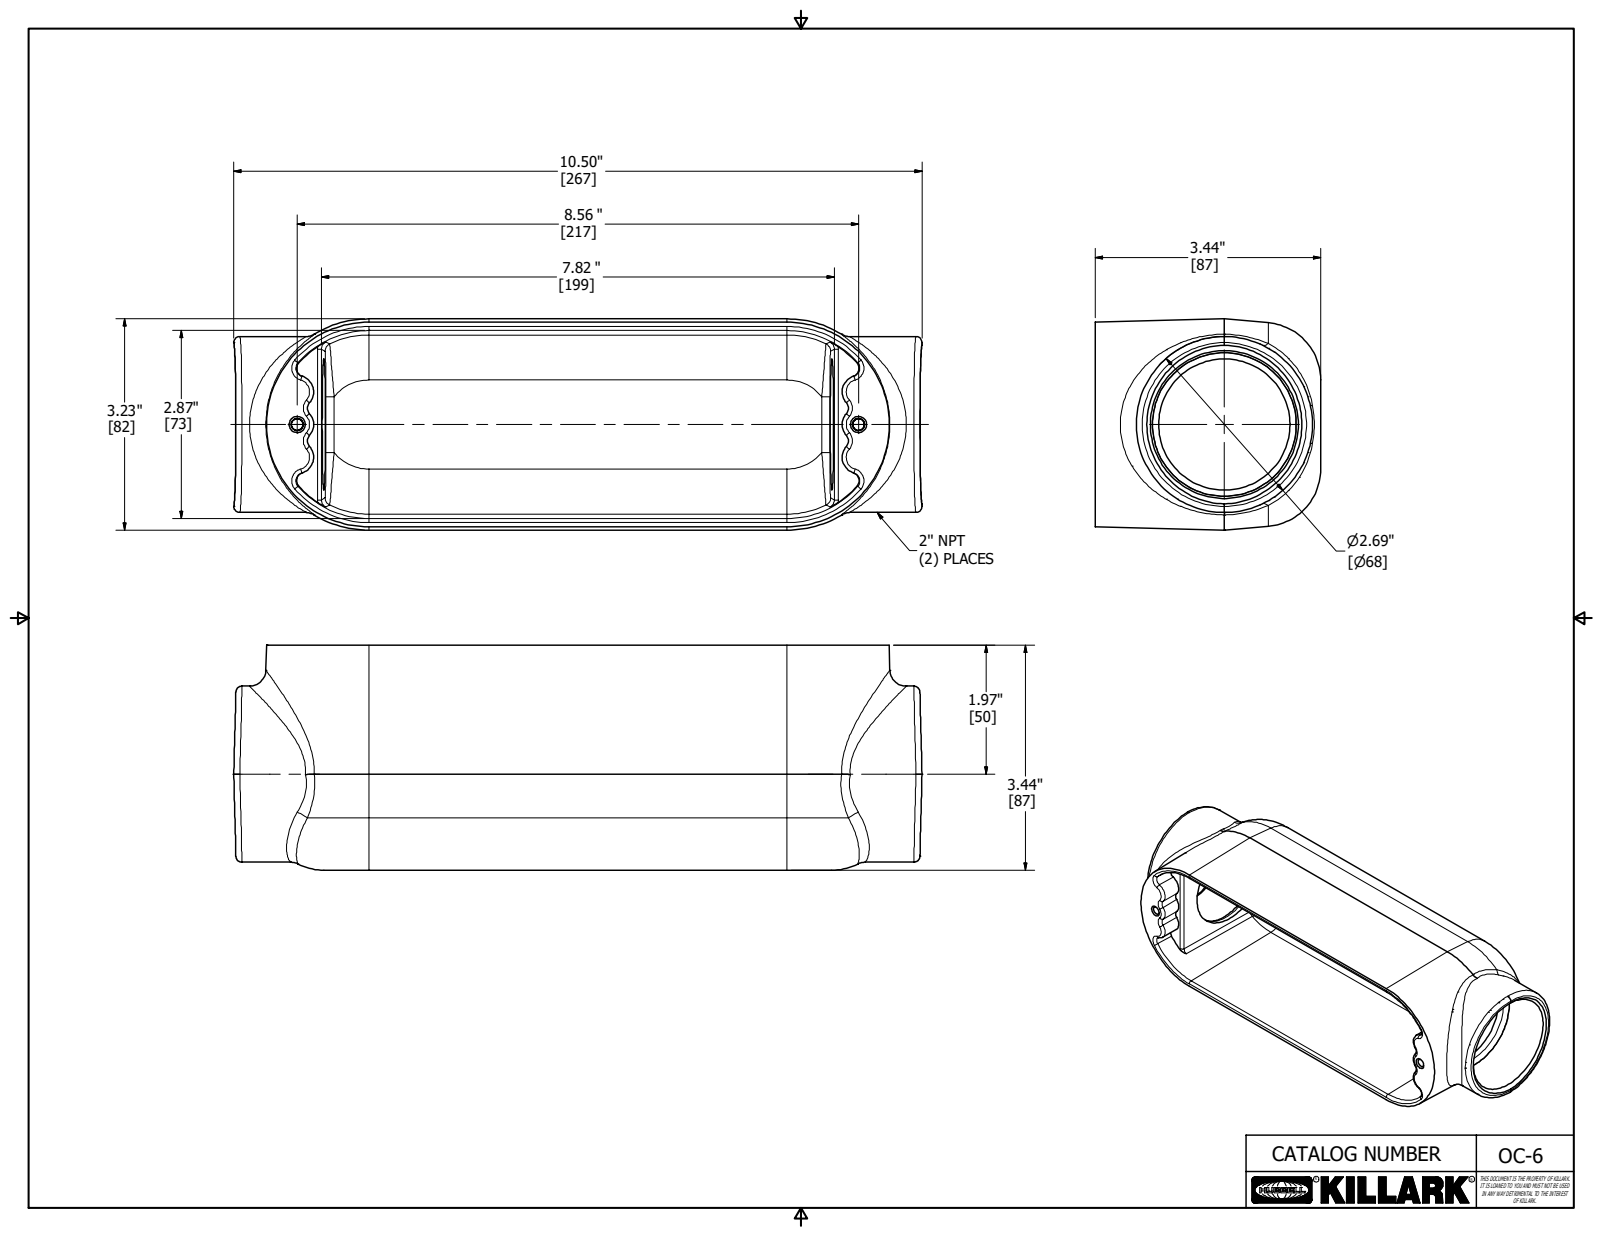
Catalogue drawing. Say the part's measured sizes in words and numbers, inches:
The part is named "18259-1". Its 3-D file was written by "Autodesk Inventor 2018 (AUTOMOTIVE_DESIGN)". It is 1 solid with 135 faces: 31 planar, 32 cylindrical and 72 other. Overall it measures 10.501 by 3.438 by 3.228 inches. Its volume is 19.49 cubic inches and its surface area 202.7 square inches. Round holes: 1 of diameter 2.004. Round bosses or shafts: 1 of diameter 2.688. Partial cylindrical surfaces (rounded edges, fillets, slot ends): 12 of radius 0.062, 6 of radius 0.125, 6 of radius 0.25, 2 of radius 0.687, 2 of radius 0.875. The main face-to-face distances are 3, 0.125, 3.313, 3.438, 0.156, 0.031, 3.281, 0.031, 0.094, 0.125.
